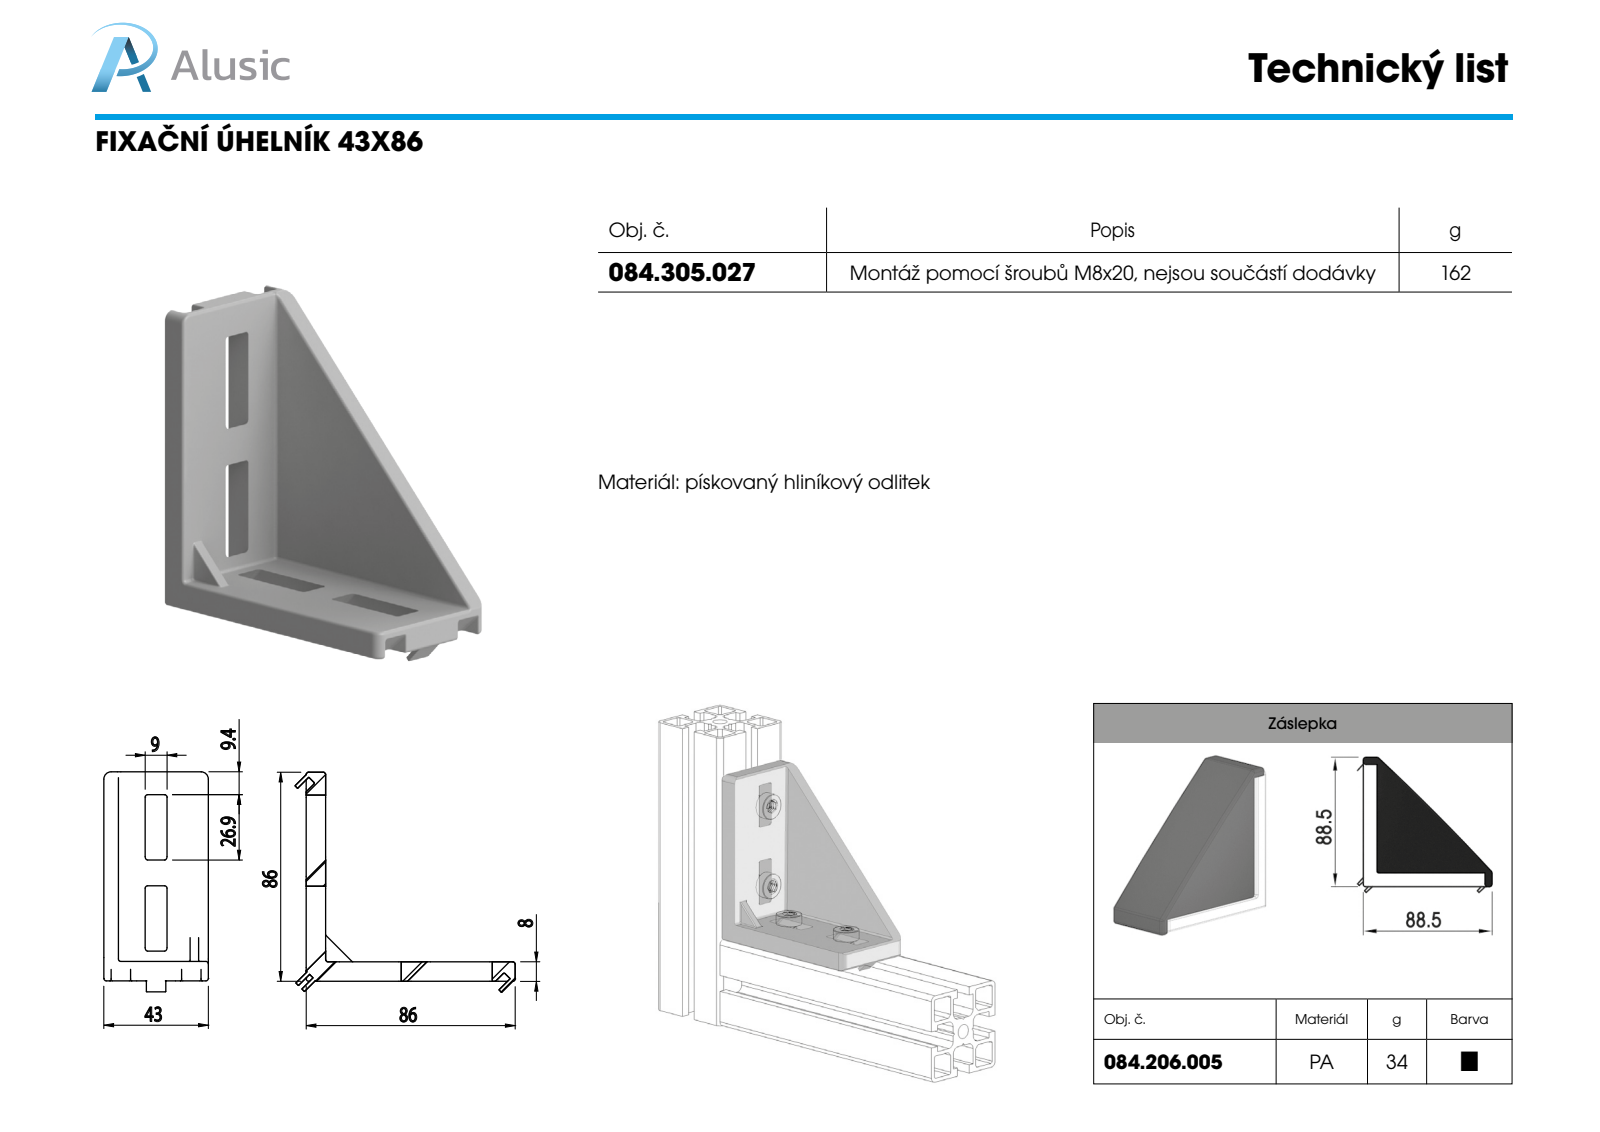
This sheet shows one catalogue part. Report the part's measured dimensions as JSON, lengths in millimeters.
{"part_name": "084.305.027", "step_written_by": "SolidWorks 2018 (CONFIG_CONTROL_DESIGN)", "units": "millimeters", "bodies": {"solids": 1, "faces": 515, "planar": 108, "cylindrical": 226, "other": 181}, "overall_size": [90.51, 90.51, 43], "volume_mm3": 53185, "surface_area_mm2": 25589, "round_bosses_or_shafts": [[4, 6]], "partial_cylinders_radius": [[0.5, 100], [0.2, 43], [1, 36], [3, 4]], "face_to_face_distances": [6, 4.5, 26, 3.5, 17, 14.5, 2.5, 8, 11, 37]}
